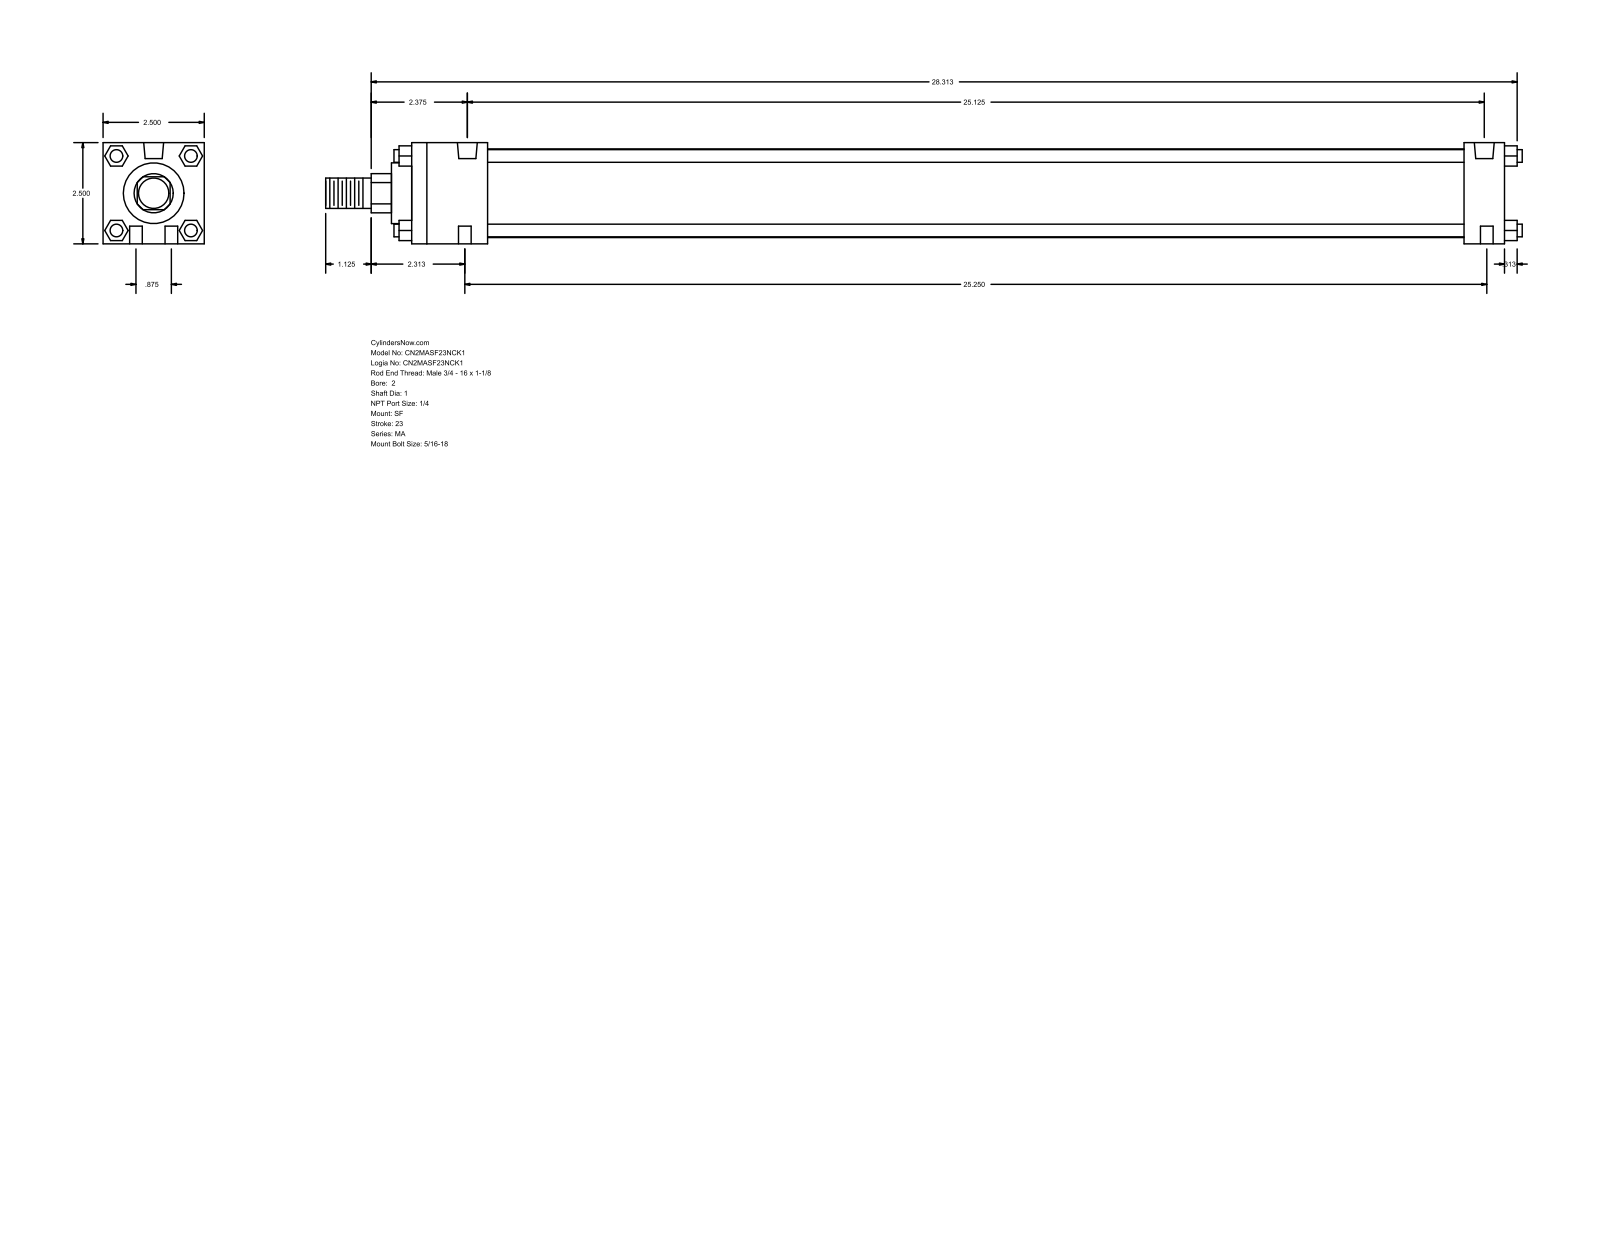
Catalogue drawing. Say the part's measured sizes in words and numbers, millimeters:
The part is named "MA_SF__0200_1". Its 3-D file was written by "GSSL Pune (CONFIG_CONTROL_DESIGN)". It is 0 solids with 124 faces: 94 planar, 30 cylindrical and 0 other. Overall it measures 750.89 by 63.5 by 63.5 millimeters. Round holes: 6 of diameter 7.94, 2 of diameter 12.49. Round bosses or shafts: 4 of diameter 7.94, 1 of diameter 55.63, 1 of diameter 38.1, 1 of diameter 25.4, 1 of diameter 19.05. Partial cylindrical surfaces (rounded edges, fillets, slot ends): 1 of radius 12.29. The main face-to-face distances are 63.5, 685.8, 12.7, 25.4, 660.4, 47.63, 612.77, 638.17, 23.37, 40.47. The hole center spacings are 11.22, 639.86, 22.22, 638.17, 641.35, 641.73.
